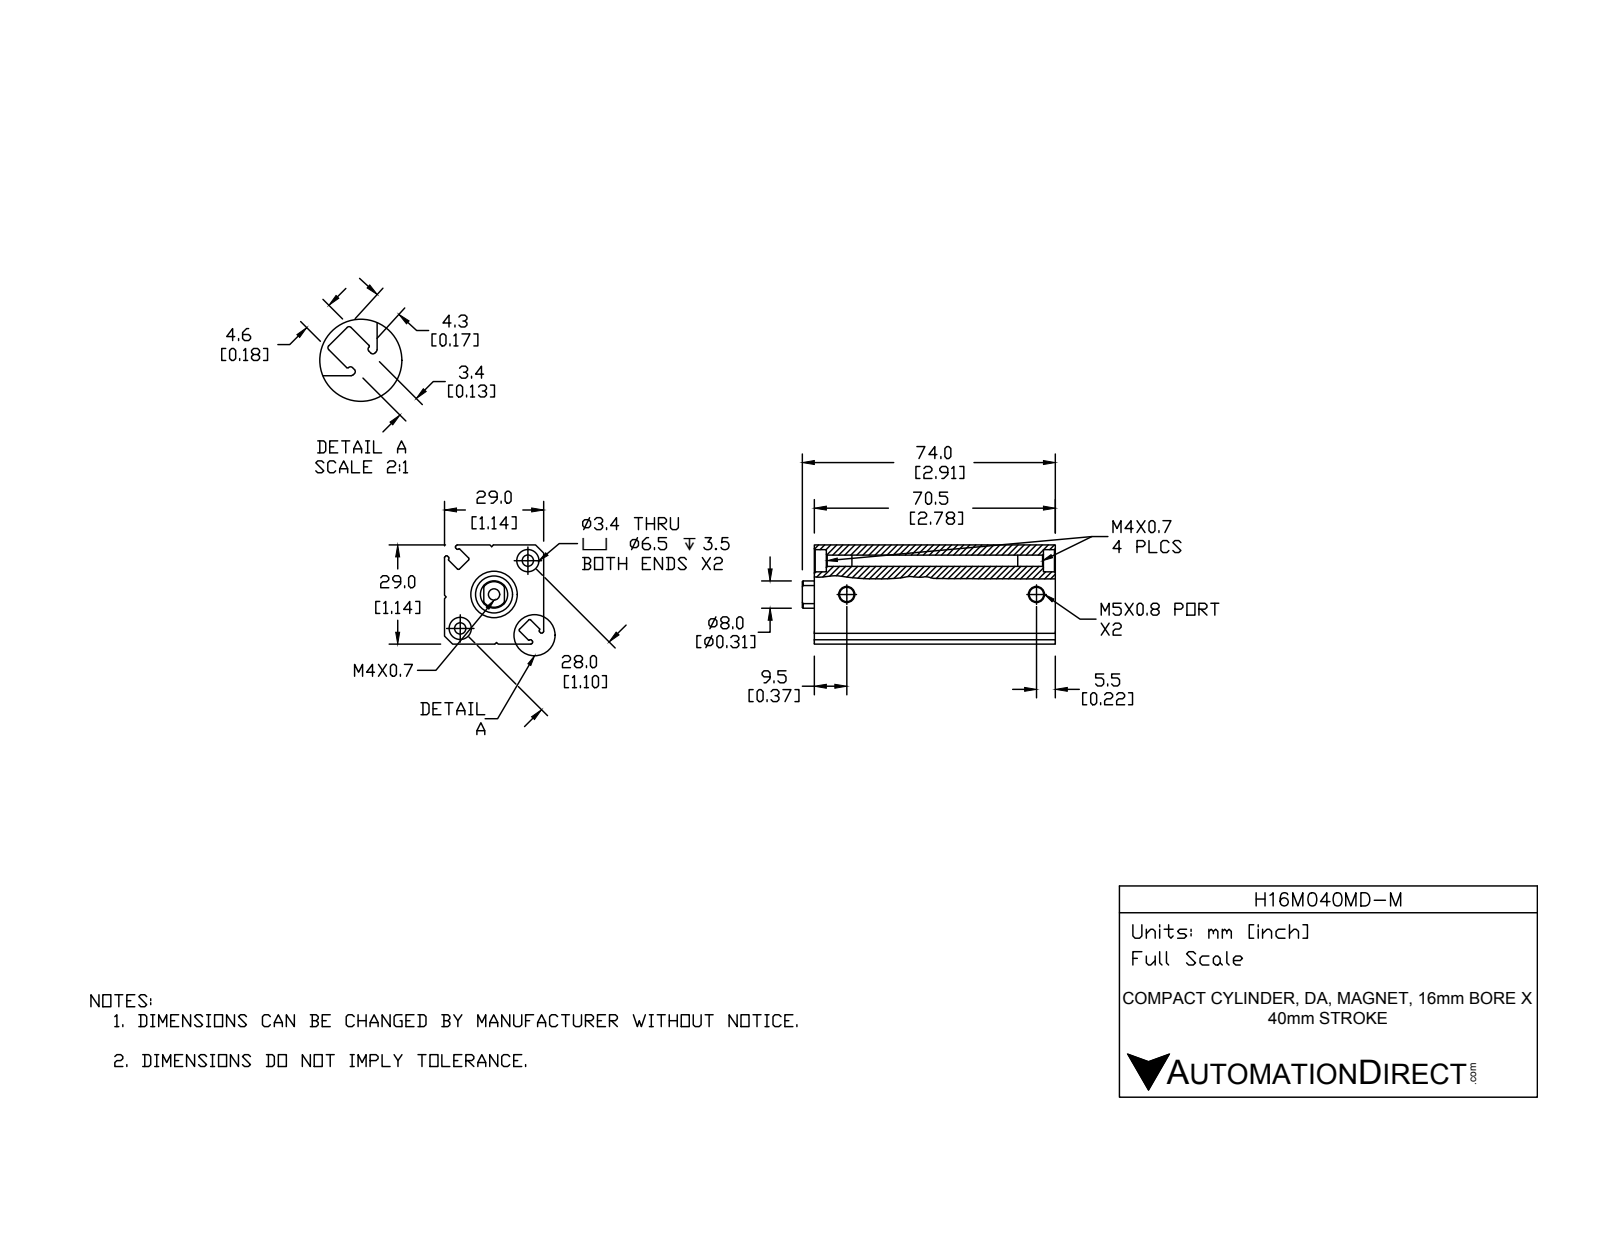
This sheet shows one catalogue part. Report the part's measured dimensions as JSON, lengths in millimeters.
{"part_name": "H16M040MD-M-BODY; H16M040MD-M-PISTON; H16M040MD-M", "step_written_by": "SolidWorks 2015 (CONFIG_CONTROL_DESIGN)", "units": "millimeters", "bodies": {"solids": 2, "faces": 128, "planar": 49, "cylindrical": 54, "other": 25}, "overall_size": [74, 29, 29], "volume_mm3": 46530, "surface_area_mm2": 18942, "round_holes": [[3.3, 3], [4.2, 2], [6.5, 2], [8, 1], [13.6, 1], [16, 1]], "round_bosses_or_shafts": [[10.8, 1]], "partial_cylinders_radius": [[0.4, 16], [0.2, 4]], "face_to_face_distances": [29, 70.5, 4, 4.6, 16.53, 21.13, 66.5, 24.84, 37.66, 20.2], "hole_center_spacings": [14, 28, 55.5]}
